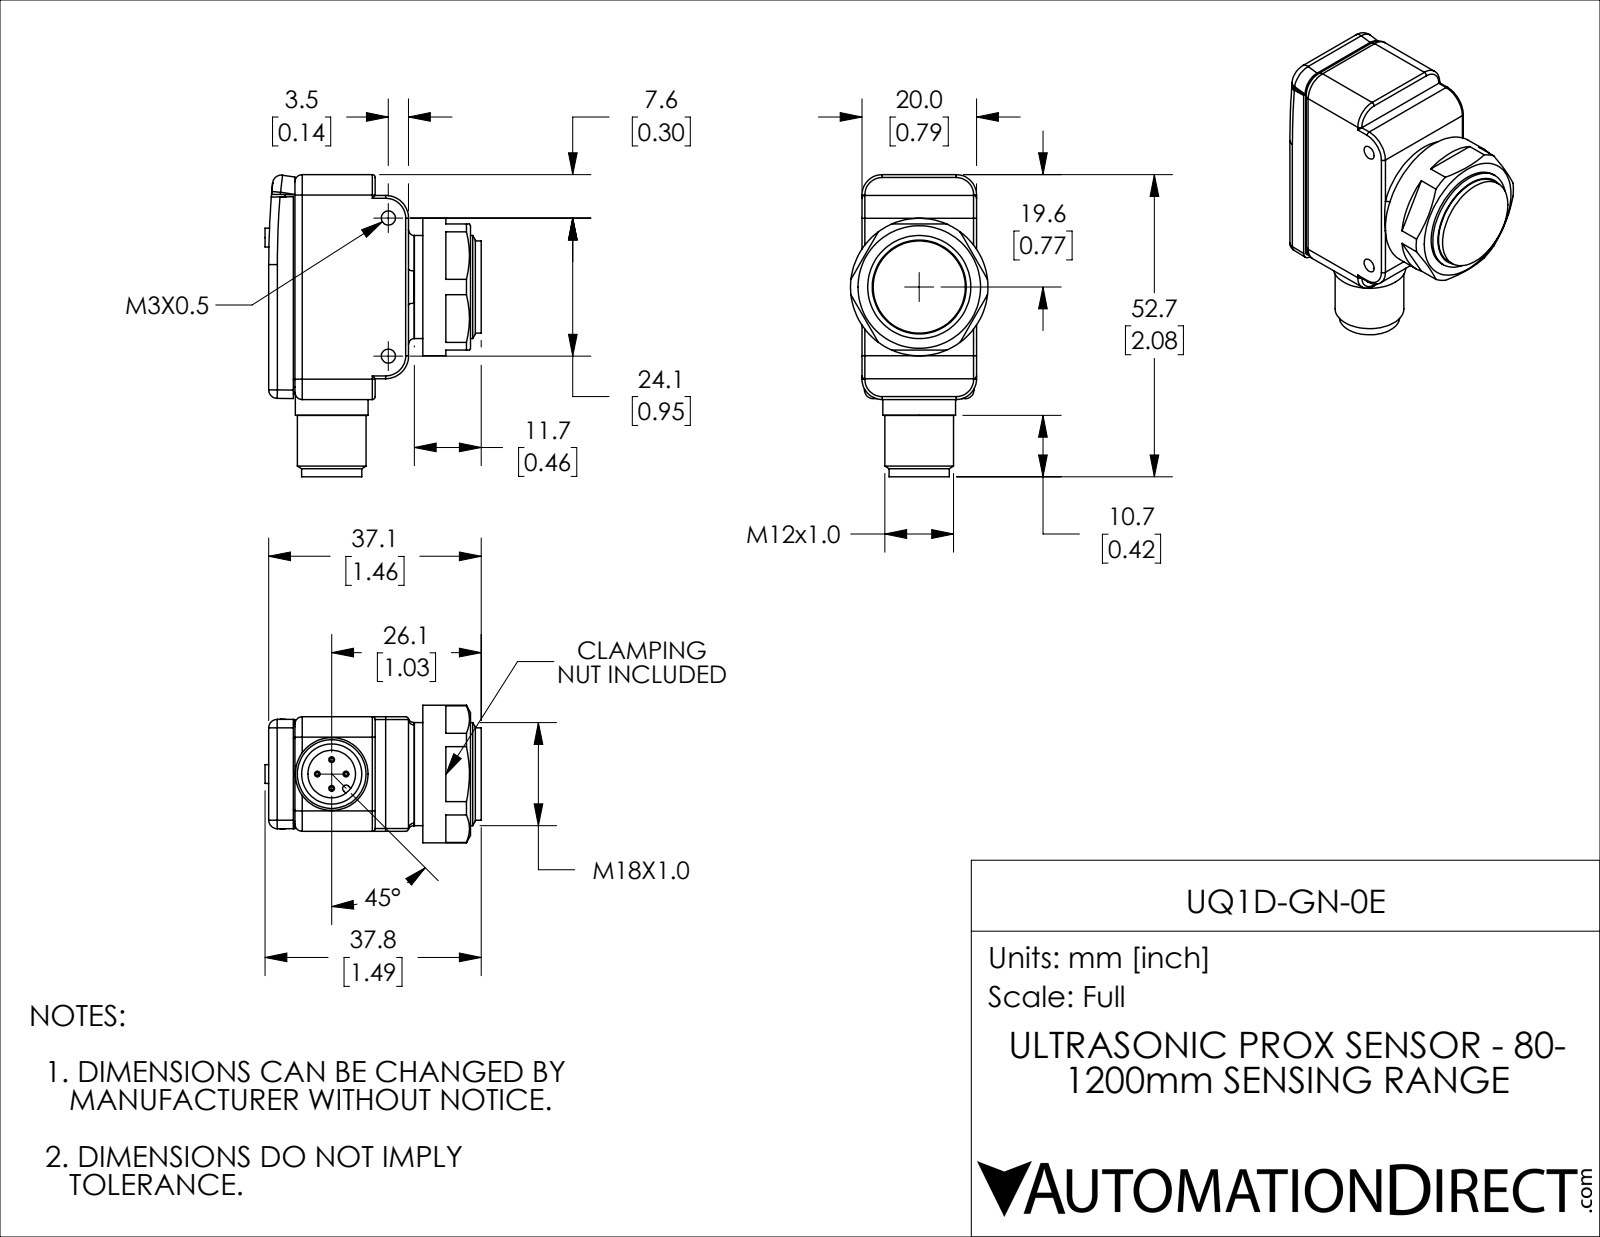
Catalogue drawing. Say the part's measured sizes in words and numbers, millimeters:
The part is named "UQ1D-GN-0E". Its 3-D file was written by "SolidWorks 2018 (AUTOMOTIVE_DESIGN)". It is 7 solids with 203 faces: 81 planar, 72 cylindrical and 50 other. Overall it measures 52.73 by 37.75 by 24 millimeters. Its volume is 22 757 cubic millimeters and its surface area 11 051 square millimeters. Round holes: 2 of diameter 2.46, 1 of diameter 3.3, 1 of diameter 8.3. Round bosses or shafts: 4 of diameter 1, 1 of diameter 24, 1 of diameter 18, 1 of diameter 16.1, 1 of diameter 12.7, 1 of diameter 12, 1 of diameter 10.5. Partial cylindrical surfaces (rounded edges, fillets, slot ends): 10 of radius 0.5, 6 of radius 1.5, 4 of radius 1.25, 4 of radius 3.55, 2 of radius 3, 2 of radius 4, 2 of radius 150, 1 of radius 0.6. The main face-to-face distances are 2.3, 20, 23.13, 20.83, 2.29, 4.59, 25.42, 11.67, 37.09, 34.8. The hole center spacings are 24.1.
